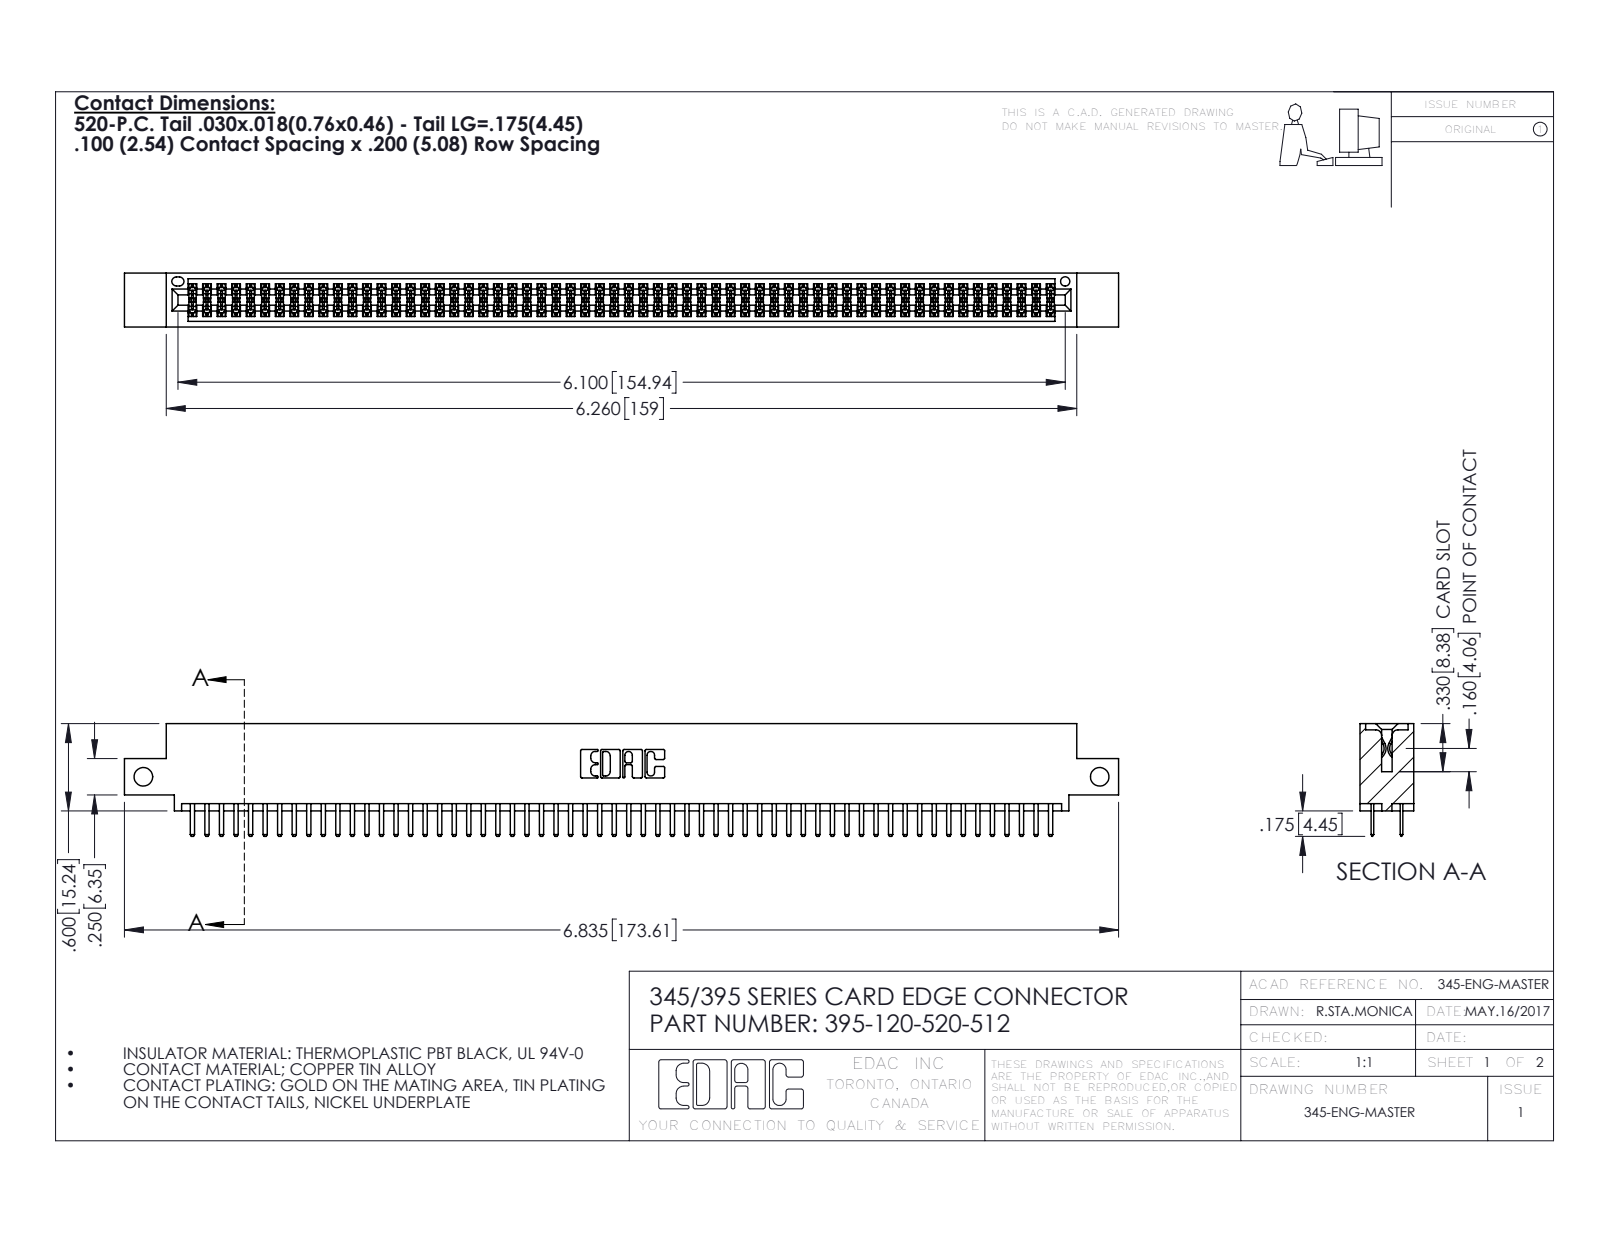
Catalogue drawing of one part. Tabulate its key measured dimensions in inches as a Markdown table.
| quantity | value |
| --- | --- |
| part name | 345 Part_0.110 Offset - Side Mount; 345-292-001_345-293-120; 395-120-520-512 |
| STEP written by | SolidWorks 2016 (CONFIG_CONTROL_DESIGN) |
| units | inches |
| bodies | 121 solids, 6610 faces (4284 planar, 2326 cylindrical, 0 other) |
| overall size | 6.835 × 0.775 × 0.37 |
| volume | 1.026 in³ |
| surface area | 38.83 in² |
| round holes (diameter × count) | 0.128 × 2, 0.064 × 1 |
| partial cylindrical surfaces (radius × count) | 0.006 × 180, 0.01 × 124, 0.01 × 22, 0.007 × 6, 0.031 × 6, 0.026 × 3, 0.014 × 2, 0.019 × 2 |
| main face-to-face distances | 0.072, 0.298, 0.2, 0.37, 0.098, 0.272, 0.025, 0.225, 0.022, 0.072 |
| hole center spacings | 6.575 |
